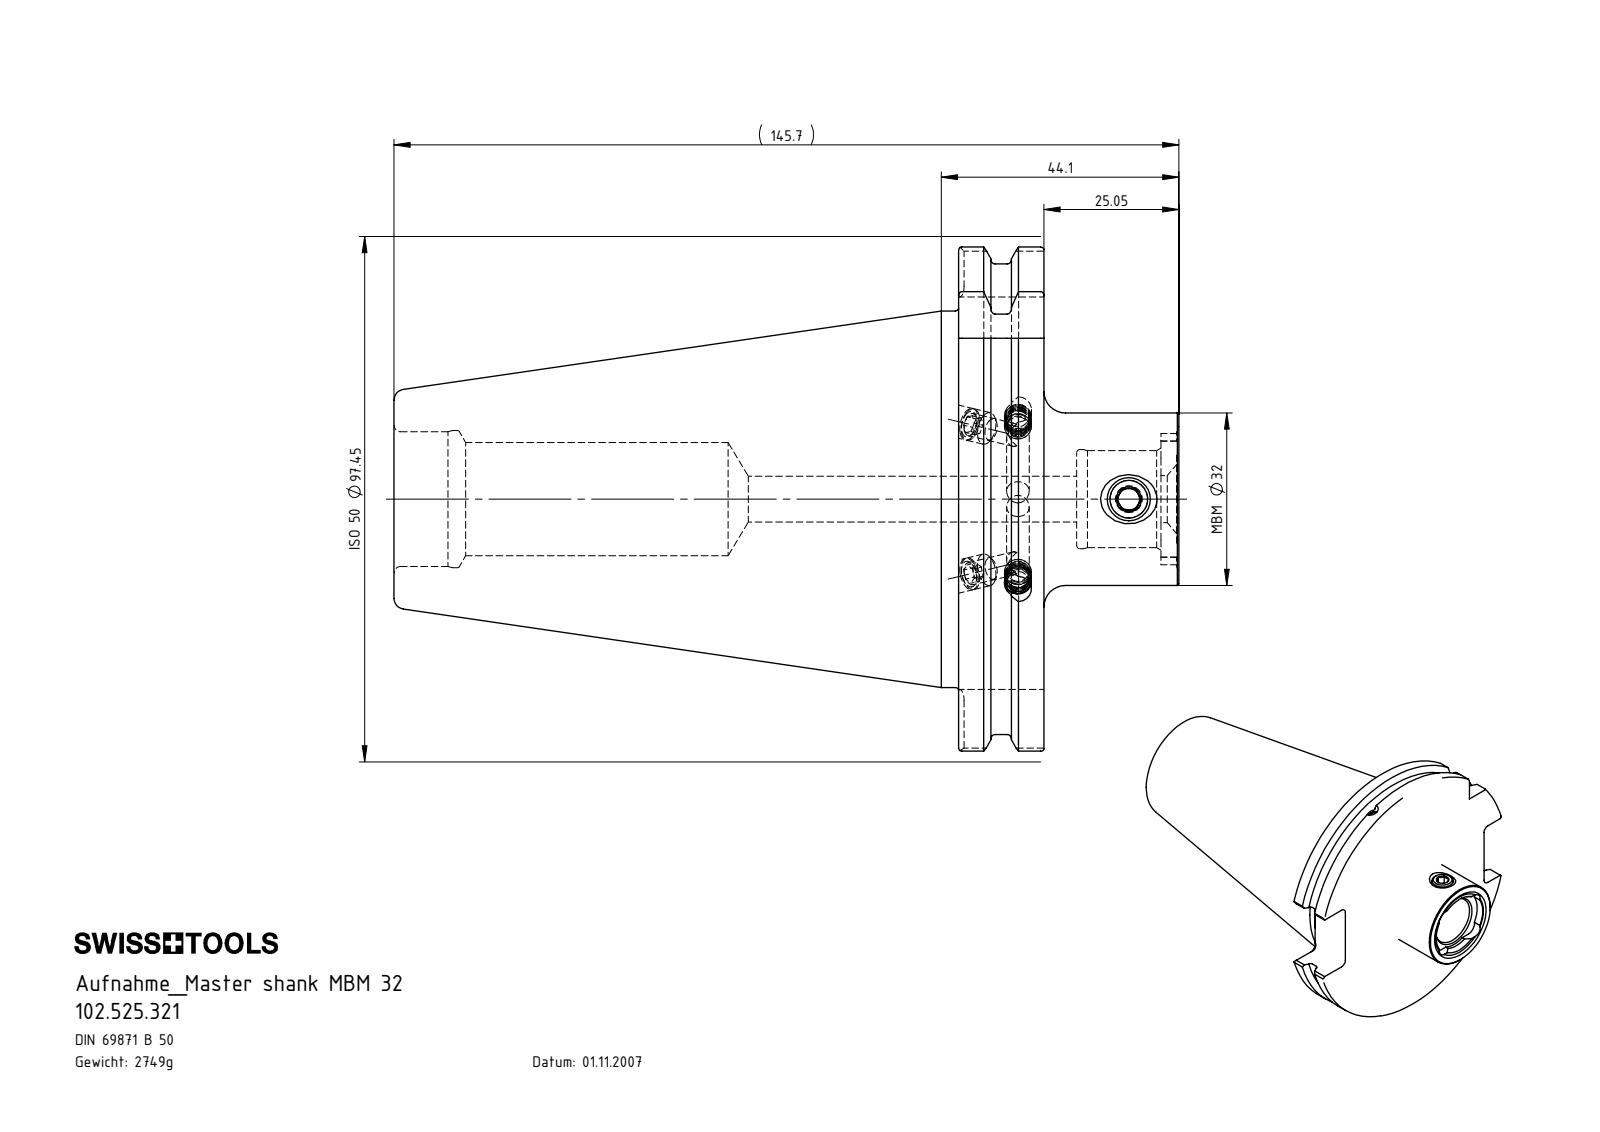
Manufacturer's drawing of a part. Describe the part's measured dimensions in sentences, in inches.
The part is named "ISO 4026 - M6 x 5_PreviewCfg; KVT_MB_600_050; 102.525.321; MB3-ER1.001.011_A (+1 more)". Its 3-D file was written by "SolidWorks 2017 (CONFIG_CONTROL_DESIGN)". It is 8 solids with 299 faces: 79 planar, 82 cylindrical and 138 other. Overall it measures 5.736 by 3.837 by 3.681 inches. Its volume is 21.38 cubic inches and its surface area 73.14 square inches. Round holes: 3 of diameter 0.157, 3 of diameter 0.165, 2 of diameter 0.236, 1 of diameter 0.197, 1 of diameter 0.276, 1 of diameter 0.335, 1 of diameter 0.709, 1 of diameter 0.724, 1 of diameter 0.827, 1 of diameter 0.984, 1 of diameter 1.002. Round bosses or shafts: 2 of diameter 0.236, 1 of diameter 3.583, 1 of diameter 2.75, 1 of diameter 1.26, 1 of diameter 0.315, 1 of diameter 0.197. Partial cylindrical surfaces (rounded edges, fillets, slot ends): 8 of radius 0.079, 4 of radius 0.126, 1 of radius 0.48, 1 of radius 1.919. The main face-to-face distances are 0.624, 4.126, 4.75, 2.866, 1.012, 5.736, 1.61, 0.986, 4.988, 0.862.
